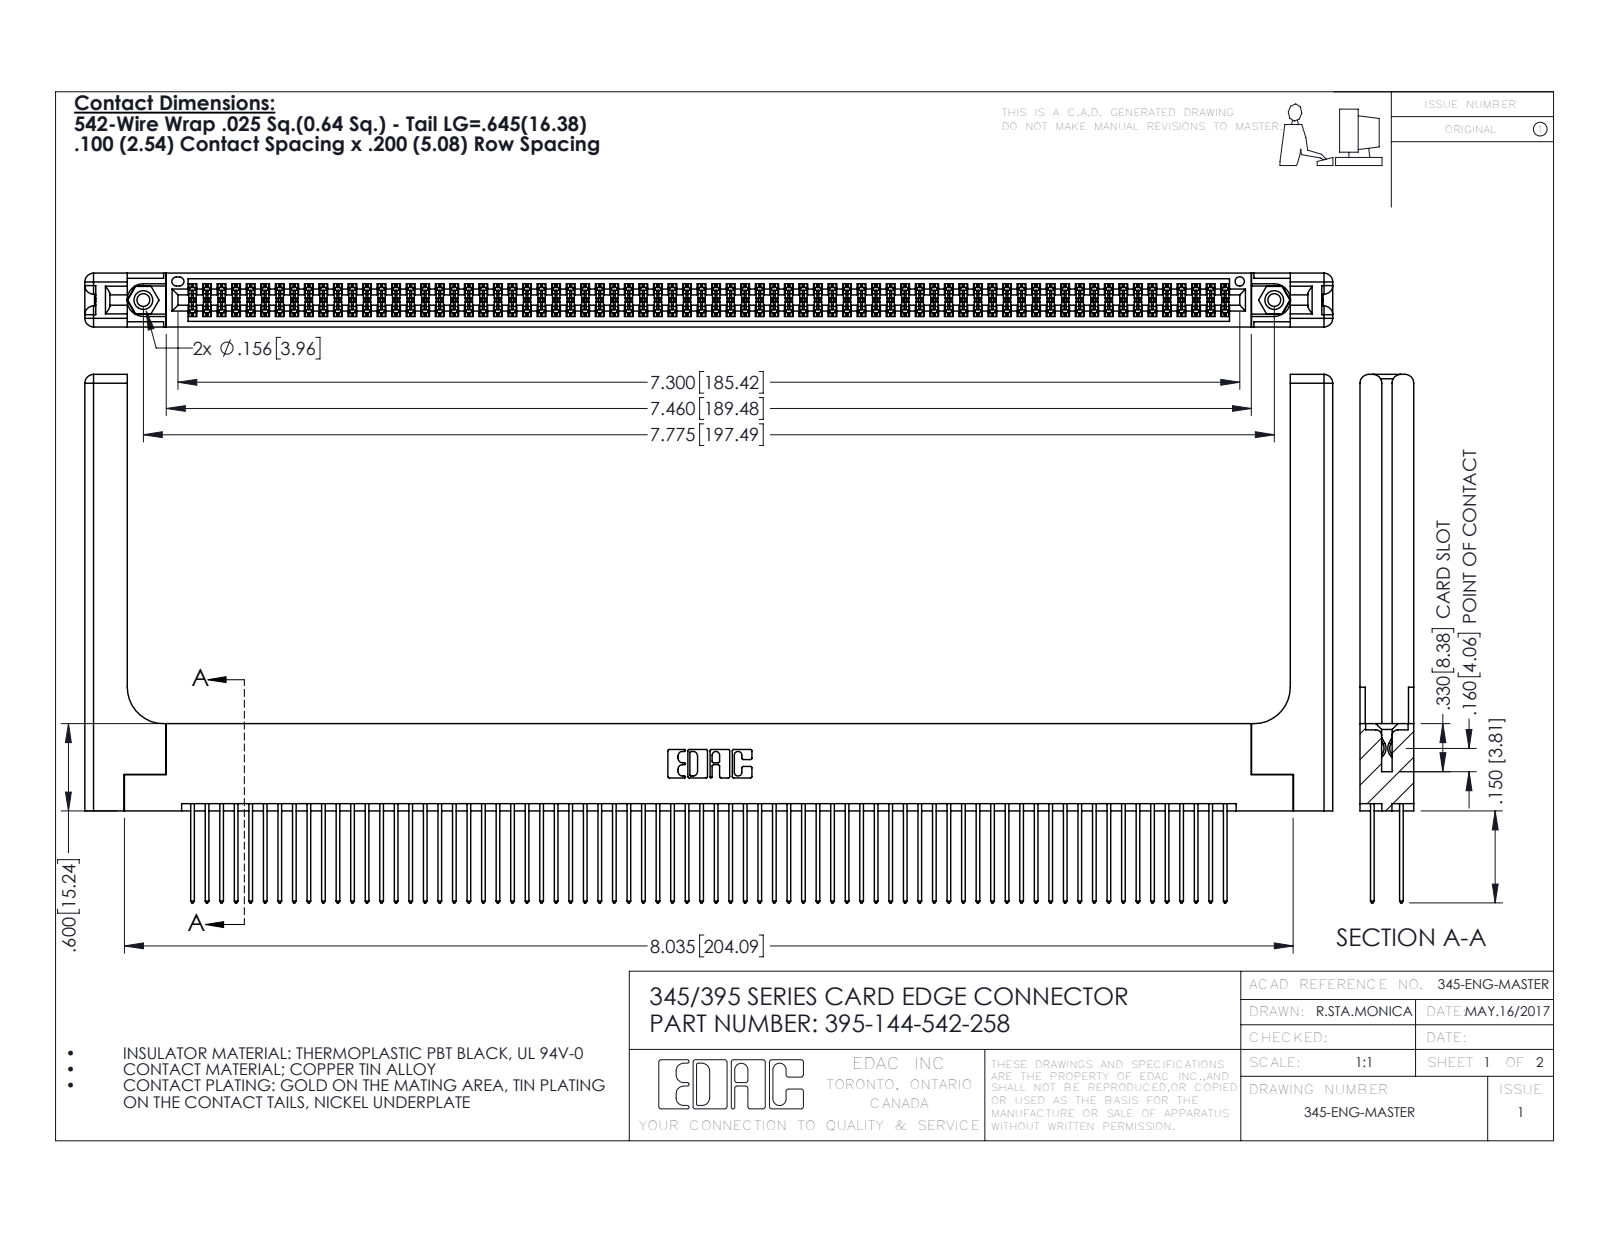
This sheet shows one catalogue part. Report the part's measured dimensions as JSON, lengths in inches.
{"part_name": "395-144-542-258; 345 Part_Flush Mounting Lugs - 0.156 Dia-TH; 345-220-058_345-220-058; 345-292-001_345-293-142 (+1 more)", "step_written_by": "SolidWorks 2016 (CONFIG_CONTROL_DESIGN)", "units": "inches", "bodies": {"solids": 149, "faces": 7582, "planar": 4980, "cylindrical": 2542, "other": 60}, "overall_size": [8.579, 3.632, 0.37], "volume_in3": 1.867, "surface_area_in2": 64.28, "round_holes": [[0.089, 2], [0.125, 2], [0.156, 2], [0.064, 1]], "round_bosses_or_shafts": [[0.155, 2]], "partial_cylinders_radius": [[0.006, 216], [0.01, 144], [0.01, 22], [0.06, 16], [0.007, 6], [0.031, 6], [0.026, 3], [0.014, 2]], "face_to_face_distances": [0.072, 0.298, 0.2, 0.098, 0.272, 0.025, 0.37, 0.225, 0.175, 0.148], "hole_center_spacings": [0.27, 7.539, 7.775]}
